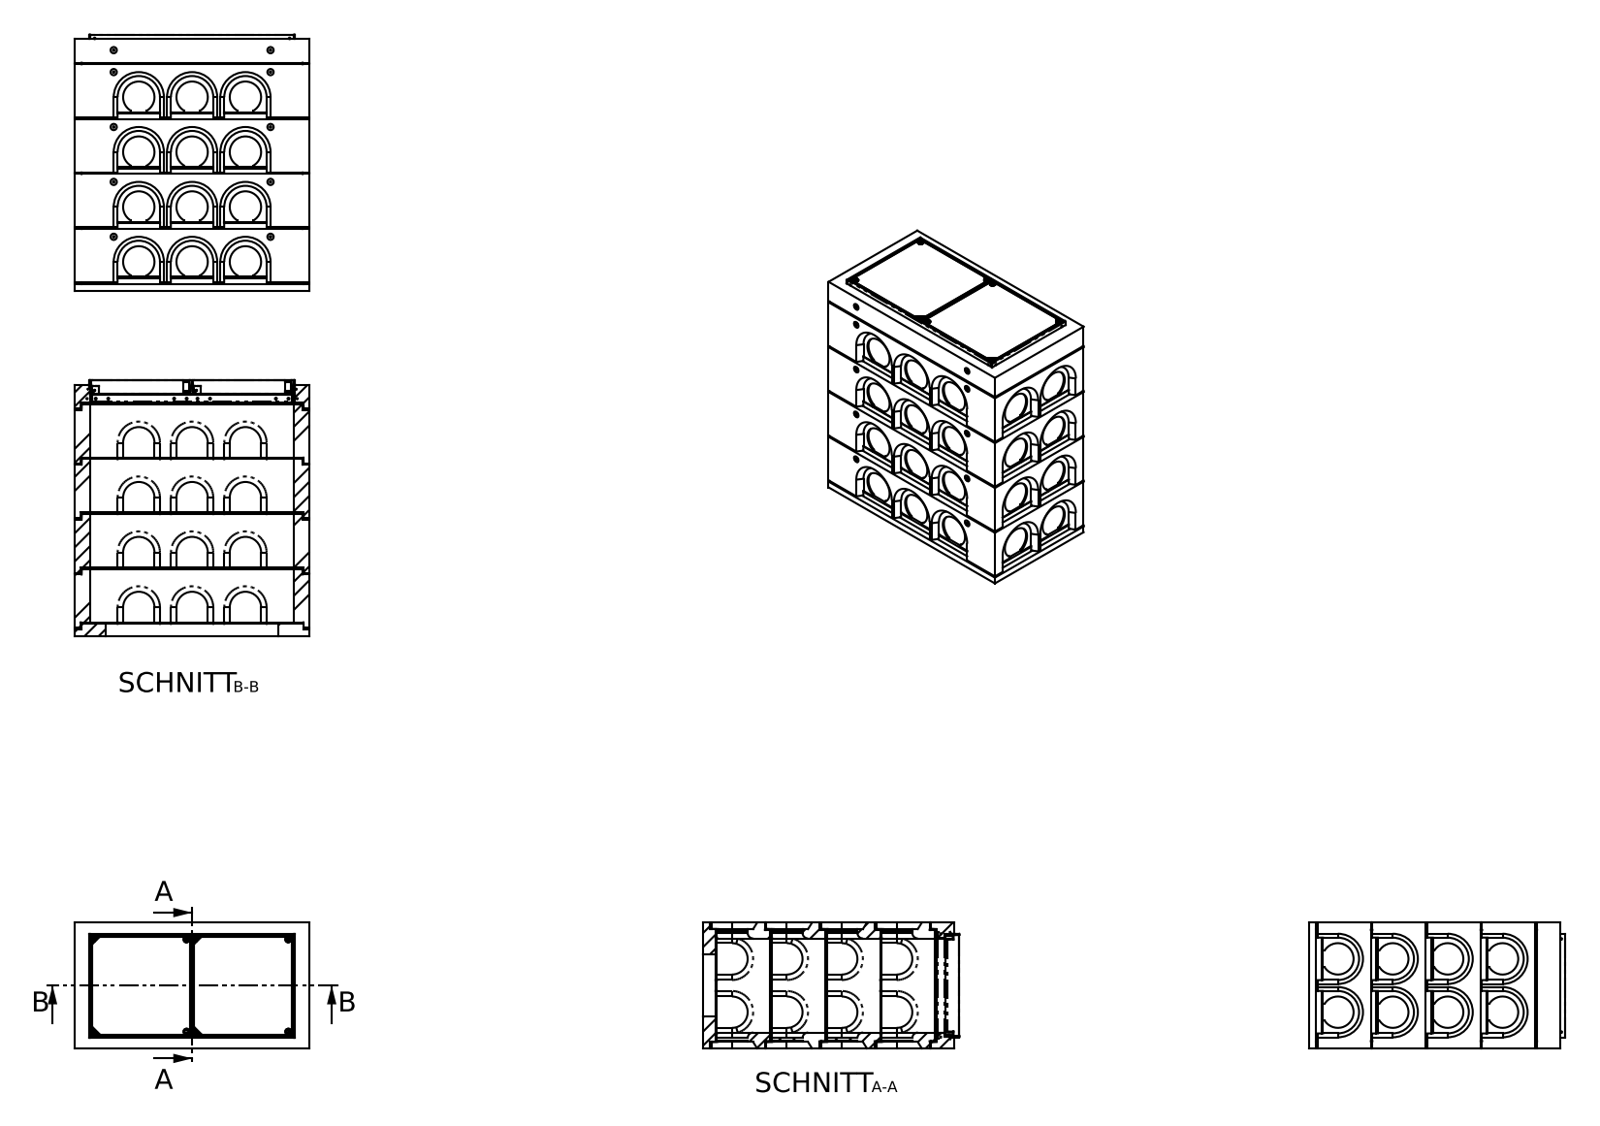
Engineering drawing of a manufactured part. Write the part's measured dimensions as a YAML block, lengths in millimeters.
part_name: "SC-ECO.0613.157.125"
step_written_by: "SolidWorks 2018 (AUTOMOTIVE_DESIGN)"
units: millimeters
bodies: {solids: 0, faces: 740, planar: 474, cylindrical: 162, other: 104}
overall_size: [1635, 1500, 800]
round_holes:
  - {diameter: 200, count: 20}
  - {diameter: 40, count: 8}
  - {diameter: 10, count: 4}
  - {diameter: 26.5, count: 4}
  - {diameter: 35, count: 4}
round_bosses_or_shafts:
  - {diameter: 5.81, count: 10}
  - {diameter: 10, count: 8}
partial_cylinders:
  - {radius: 35, count: 16}
  - {radius: 2.5, count: 6}
  - {radius: 3, count: 6}
  - {radius: 5, count: 4}
  - {radius: 13.5, count: 4}
face_to_face_distances: [700, 50, 10, 350, 35, 100, 800, 25, 710, 315]
hole_center_spacings: [350, 487.95, 700, 340, 778.2, 226.27, 524.98, 855.1]
